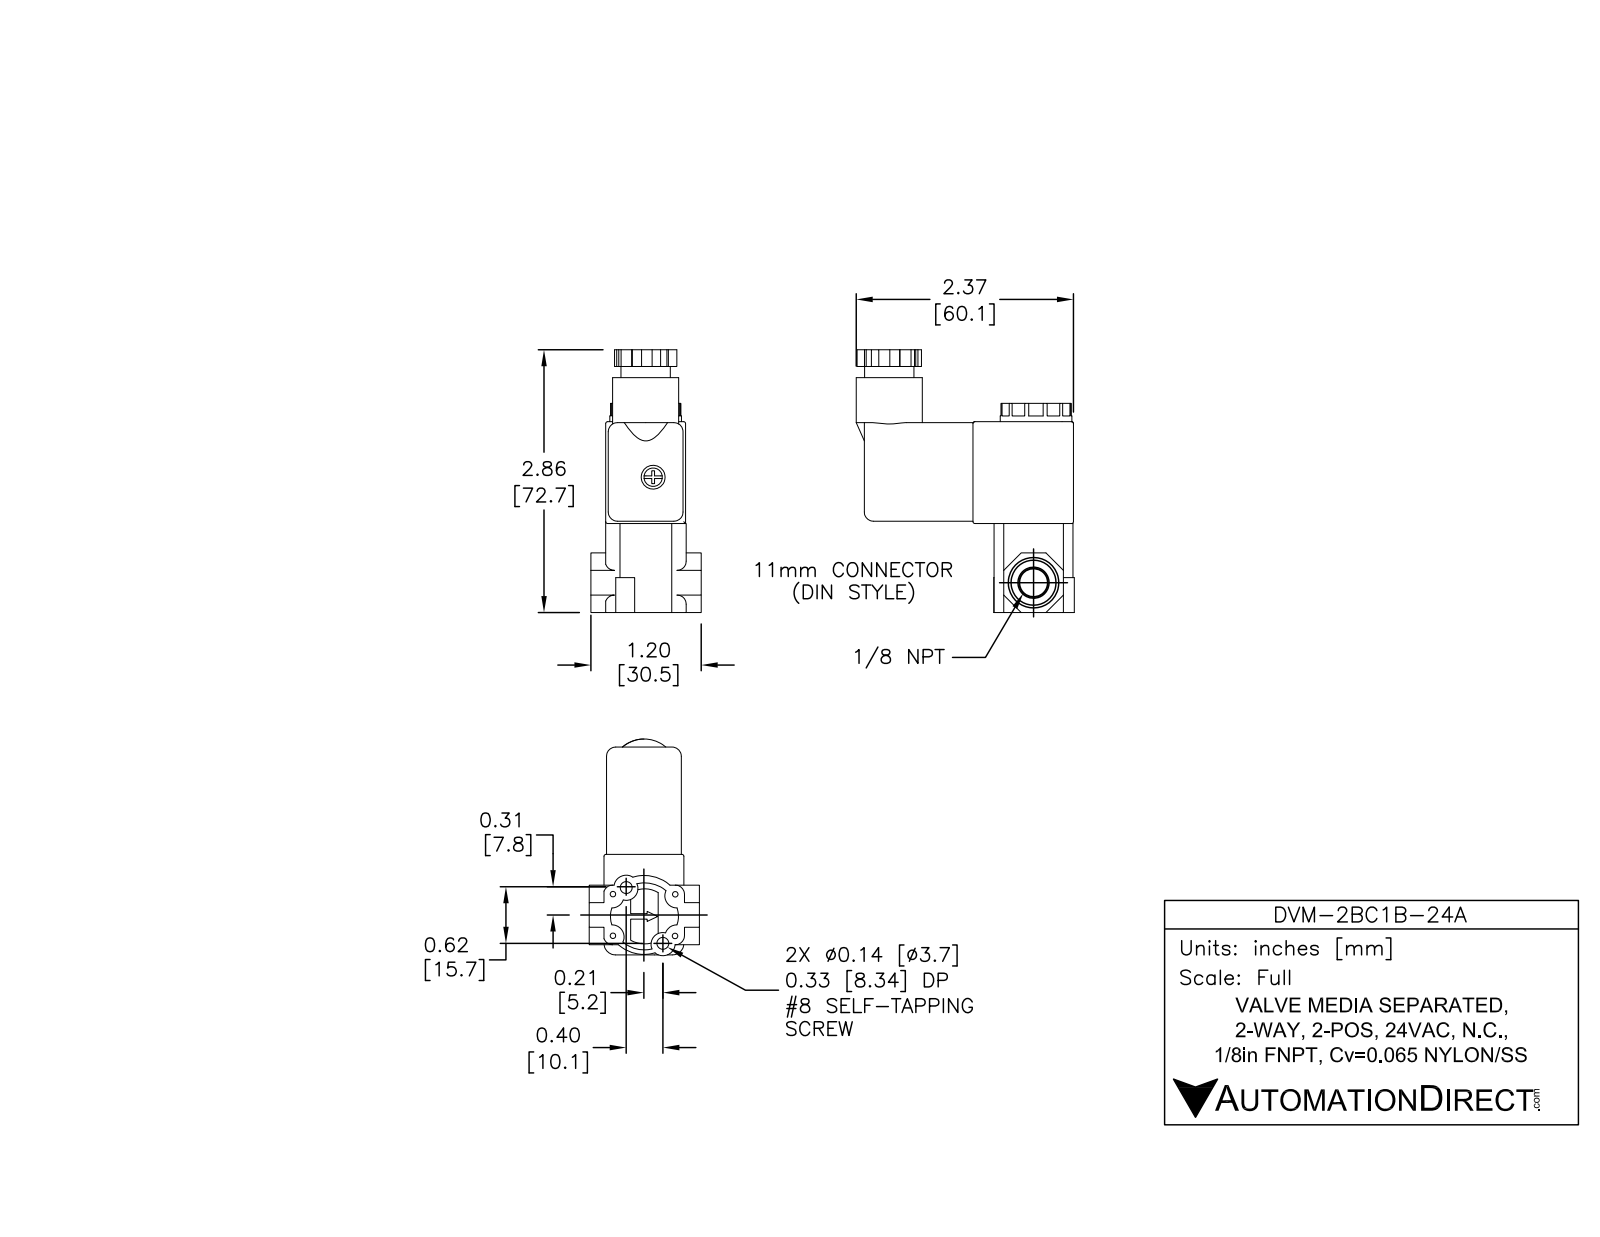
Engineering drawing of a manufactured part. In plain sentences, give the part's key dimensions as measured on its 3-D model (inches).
The part is named "DVM-2BC1B-24A". Its 3-D file was written by "SolidWorks 2015 (AUTOMOTIVE_DESIGN)". It is 1 solid with 253 faces: 133 planar, 101 cylindrical and 19 other. Overall it measures 2.914 by 2.486 by 0.878 inches. Its volume is 3.042 cubic inches and its surface area 19.9 square inches. Round holes: 2 of diameter 0.127, 2 of diameter 0.136, 2 of diameter 0.137, 2 of diameter 0.32, 1 of diameter 0.25, 1 of diameter 0.26, 1 of diameter 0.41. Round bosses or shafts: 1 of diameter 0.78, 1 of diameter 0.72, 1 of diameter 0.537, 1 of diameter 0.25, 1 of diameter 0.2. Partial cylindrical surfaces (rounded edges, fillets, slot ends): 12 of radius 0.153, 11 of radius 0.02, 11 of radius 0.1, 4 of radius 0.133, 2 of radius 0.125, 2 of radius 0.129, 2 of radius 0.135, 2 of radius 0.277. The main face-to-face distances are 0.028, 0.843, 0.87, 0.815, 2.25, 0.65, 0.2, 2.13, 1.335, 1.135. The hole center spacings are 0.448, 1.892, 0.174, 0.175, 0.339, 0.381, 0.381, 0.393.
